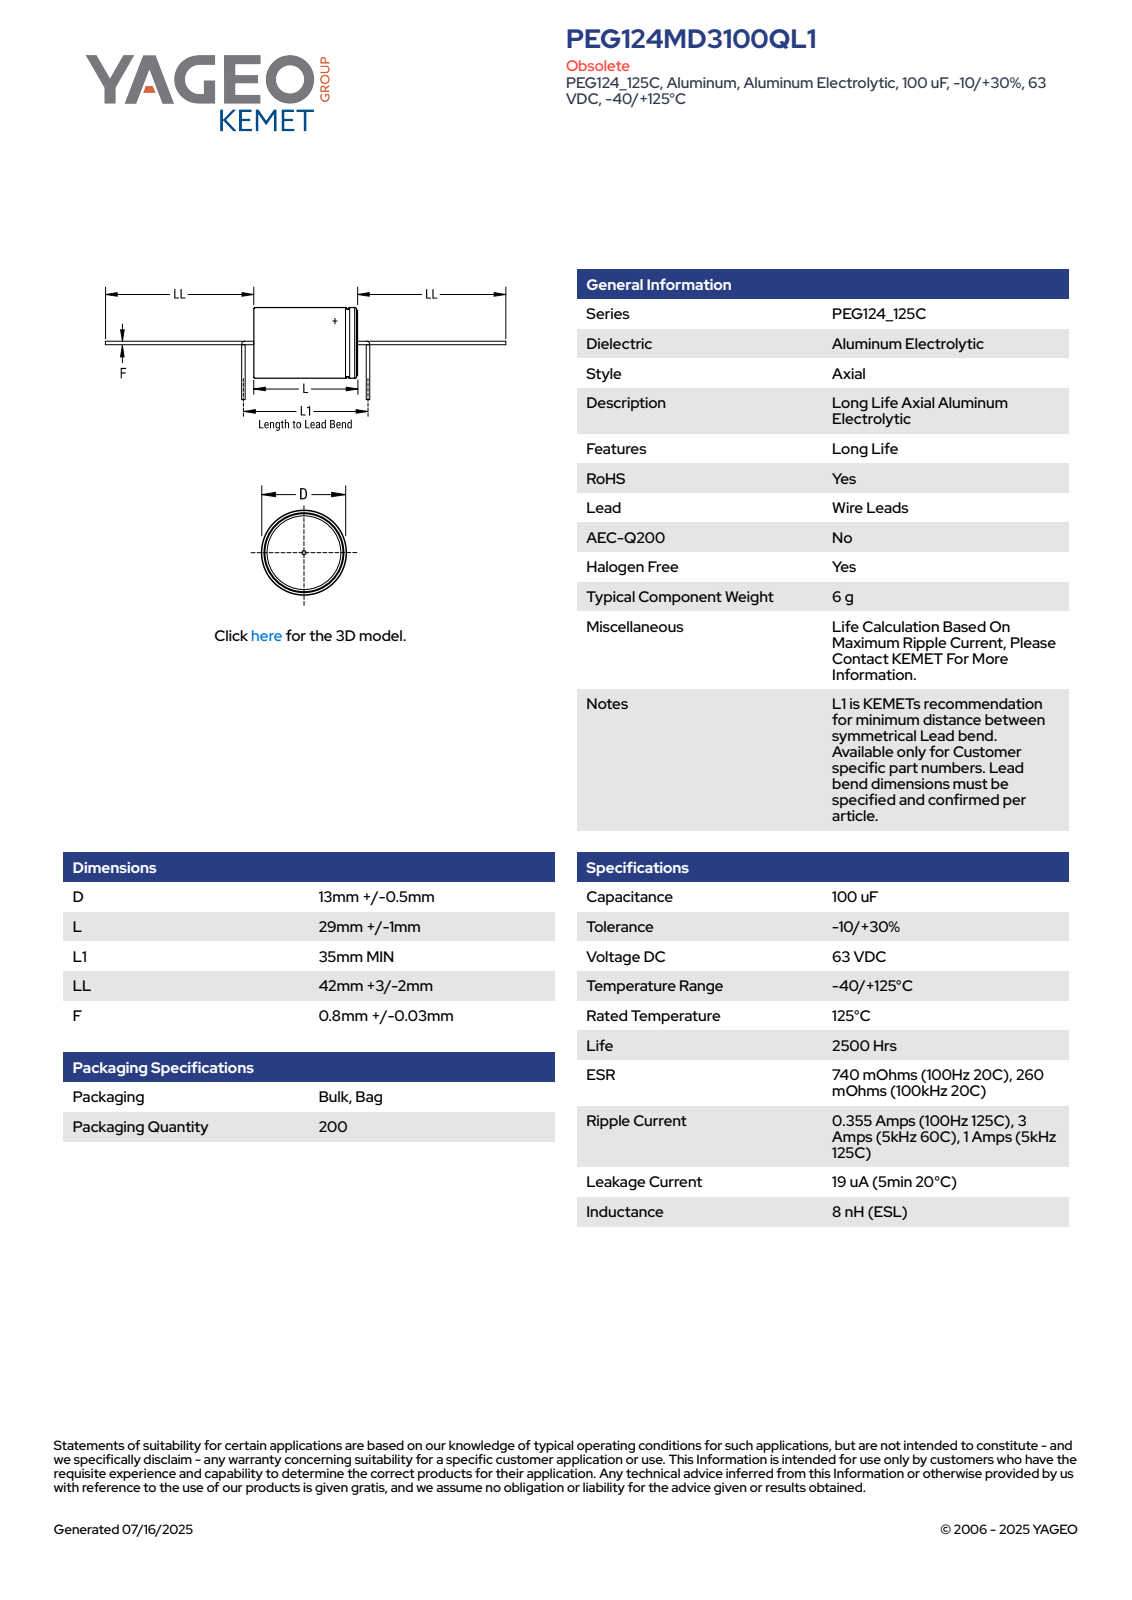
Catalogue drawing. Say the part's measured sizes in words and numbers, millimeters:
The part is named "CAA_PEG124_13X29_D13.5L30LL45F0.83". Its 3-D file was written by "SolidWorks 2014 (AUTOMOTIVE_DESIGN)". It is 1 solid with 99 faces: 27 planar, 29 cylindrical and 43 other. Overall it measures 117 by 13.5 by 13.5 millimeters. Its volume is 4 213 cubic millimeters and its surface area 1 830 square millimeters. Round holes: 1 of diameter 12.5. Round bosses or shafts: 1 of diameter 13.5, 1 of diameter 13, 1 of diameter 0.83. Partial cylindrical surfaces (rounded edges, fillets, slot ends): 1 of radius 6.74. The main face-to-face distances are 29, 30, 1, 45, 74, 75, 117, 72, 43, 42.
